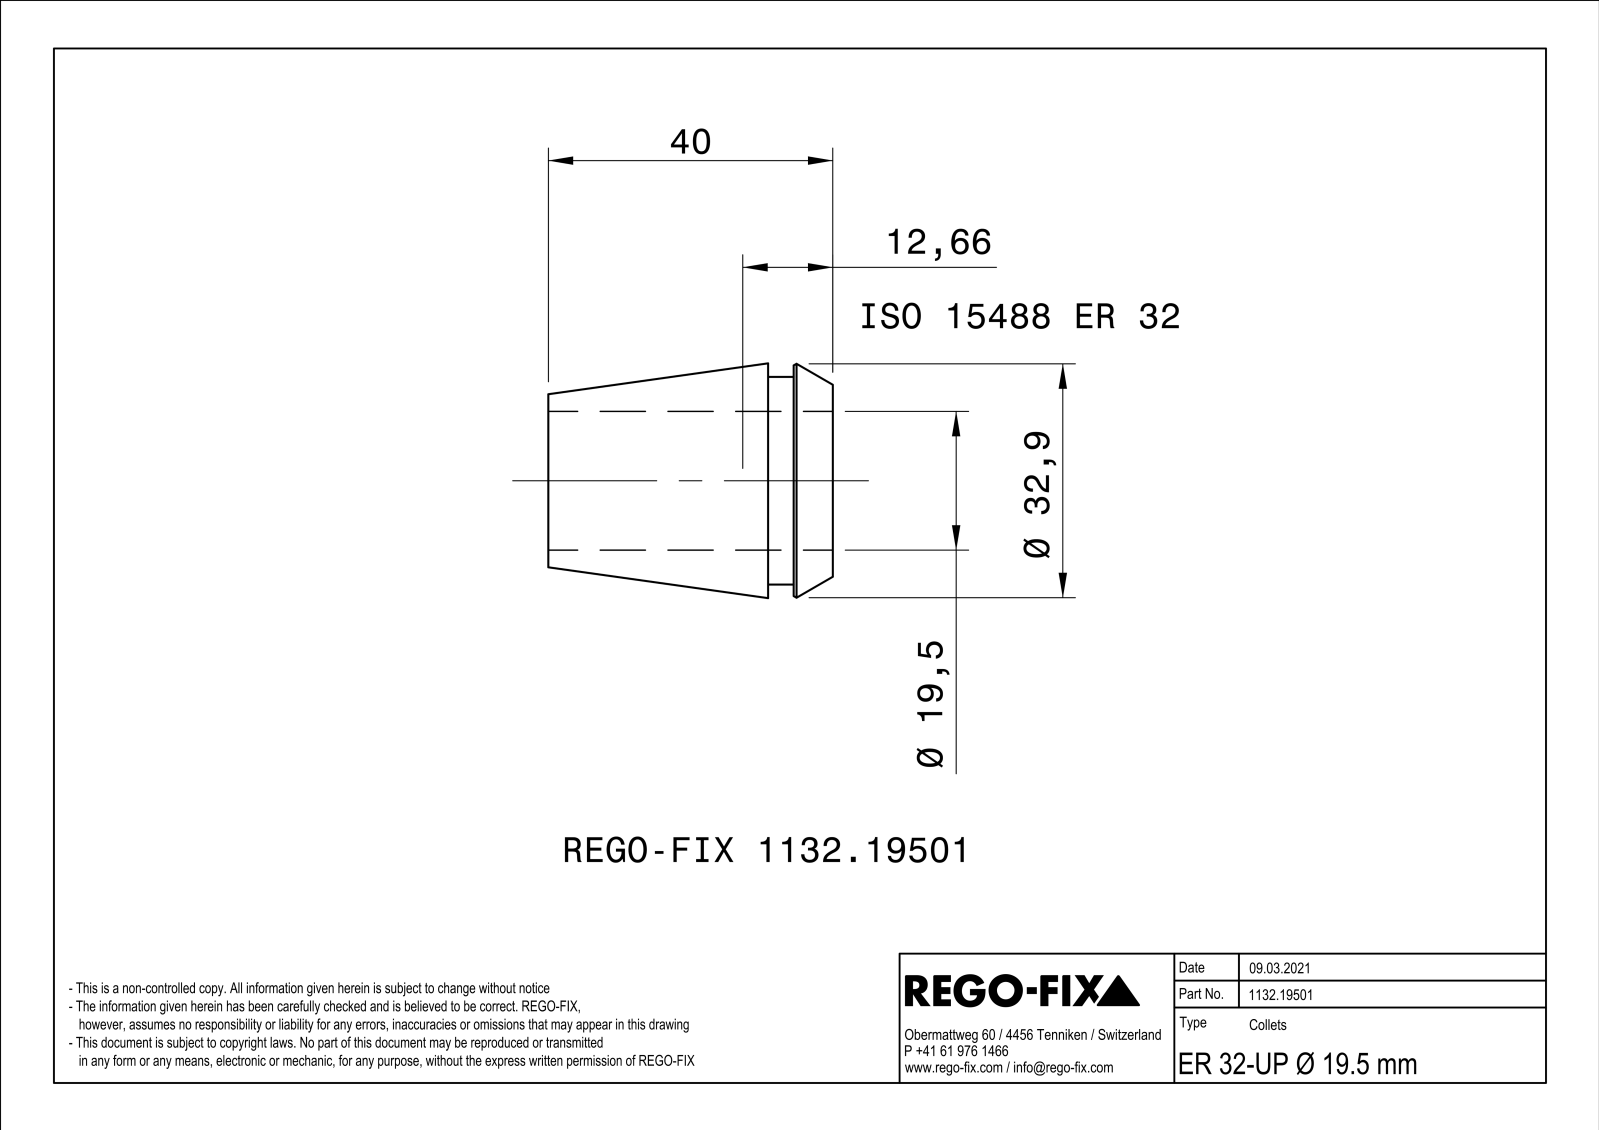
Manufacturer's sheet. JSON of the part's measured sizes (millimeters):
{"part_name": "NOCUT", "step_written_by": "SIEMENS PLM Software Solid Edge ST10 (AUTOMOTIVE_DESIGN)", "units": "millimeters", "bodies": {"solids": 1, "faces": 209, "planar": 88, "cylindrical": 41, "other": 80}, "overall_size": [40, 32.98, 32.98], "volume_mm3": 11792, "surface_area_mm2": 11138, "round_holes": [[19.5, 1]], "round_bosses_or_shafts": [[29.2, 1]], "partial_cylinders_radius": [[0.4, 20]], "face_to_face_distances": [1, 9.1, 5.5, 3.6, 40, 34.5, 30.9, 6, 0.5, 3.1]}
